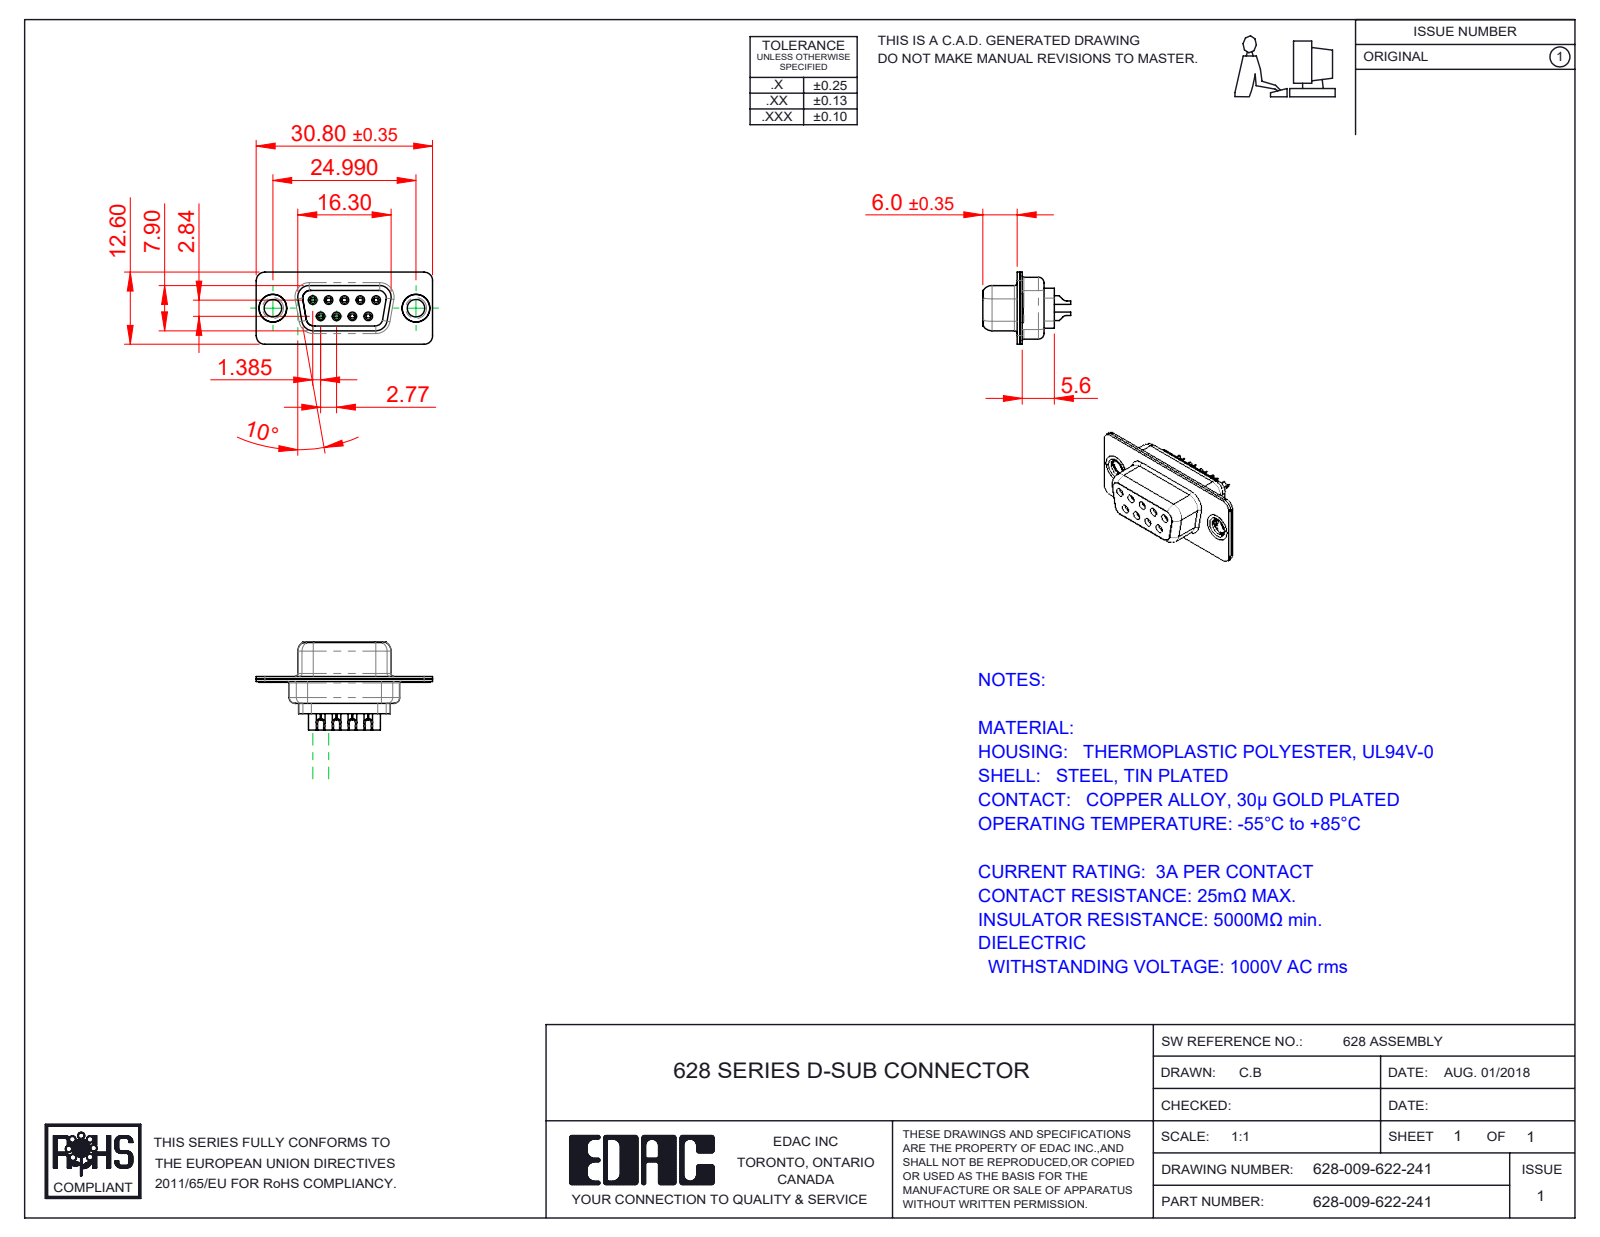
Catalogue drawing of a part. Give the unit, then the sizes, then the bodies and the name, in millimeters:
Units: millimetres
Overall size (bounding box): 30.8 × 15.35 × 12.6
Round holes (diameter × count): ⌀0.8 ×9, ⌀0.9 ×9, ⌀1.1 ×9, ⌀1.6 ×9, ⌀1.7 ×5, ⌀3.05 ×2, ⌀4 ×2, ⌀4.05 ×2, ⌀4.85 ×2
Round bosses / shafts (diameter × count): ⌀2 ×9, ⌀1.5 ×9, ⌀1.2 ×9, ⌀5 ×2, ⌀4.95 ×2, ⌀4.8 ×2, ⌀3.55 ×2
Partial cylindrical surfaces — rounded edges, fillets, slot ends (radius × count): R1.5 ×17, R2 ×12, R0.28 ×9, R1 ×6, R1.35 ×6, R0.25 ×4, R0.5 ×4, R0.6 ×4
Main face-to-face distances: 0.45, 0.4, 0.9, 1.9, 8.5, 6.6, 1.4, 7.05, 0.5, 1.05
Hole centre spacings: 3.16, 2.77, 5.54, 5.03, 5.04, 8.31, 7.48, 7.49
Volume: 1 684 mm³ · Surface area: 4 380 mm²
Bodies: 14 solids, 1054 faces (256 planar, 346 cylindrical, 452 other)
Part name (STEP PRODUCT): 628 Shell Rear_09 Contacts; 628 Thru Hole Rivet; 628 Shell Front_09 Contacts; 628 Contact Row 2_22L (+3 more)
STEP written by: SolidWorks 2020 (CONFIG_CONTROL_DESIGN)
